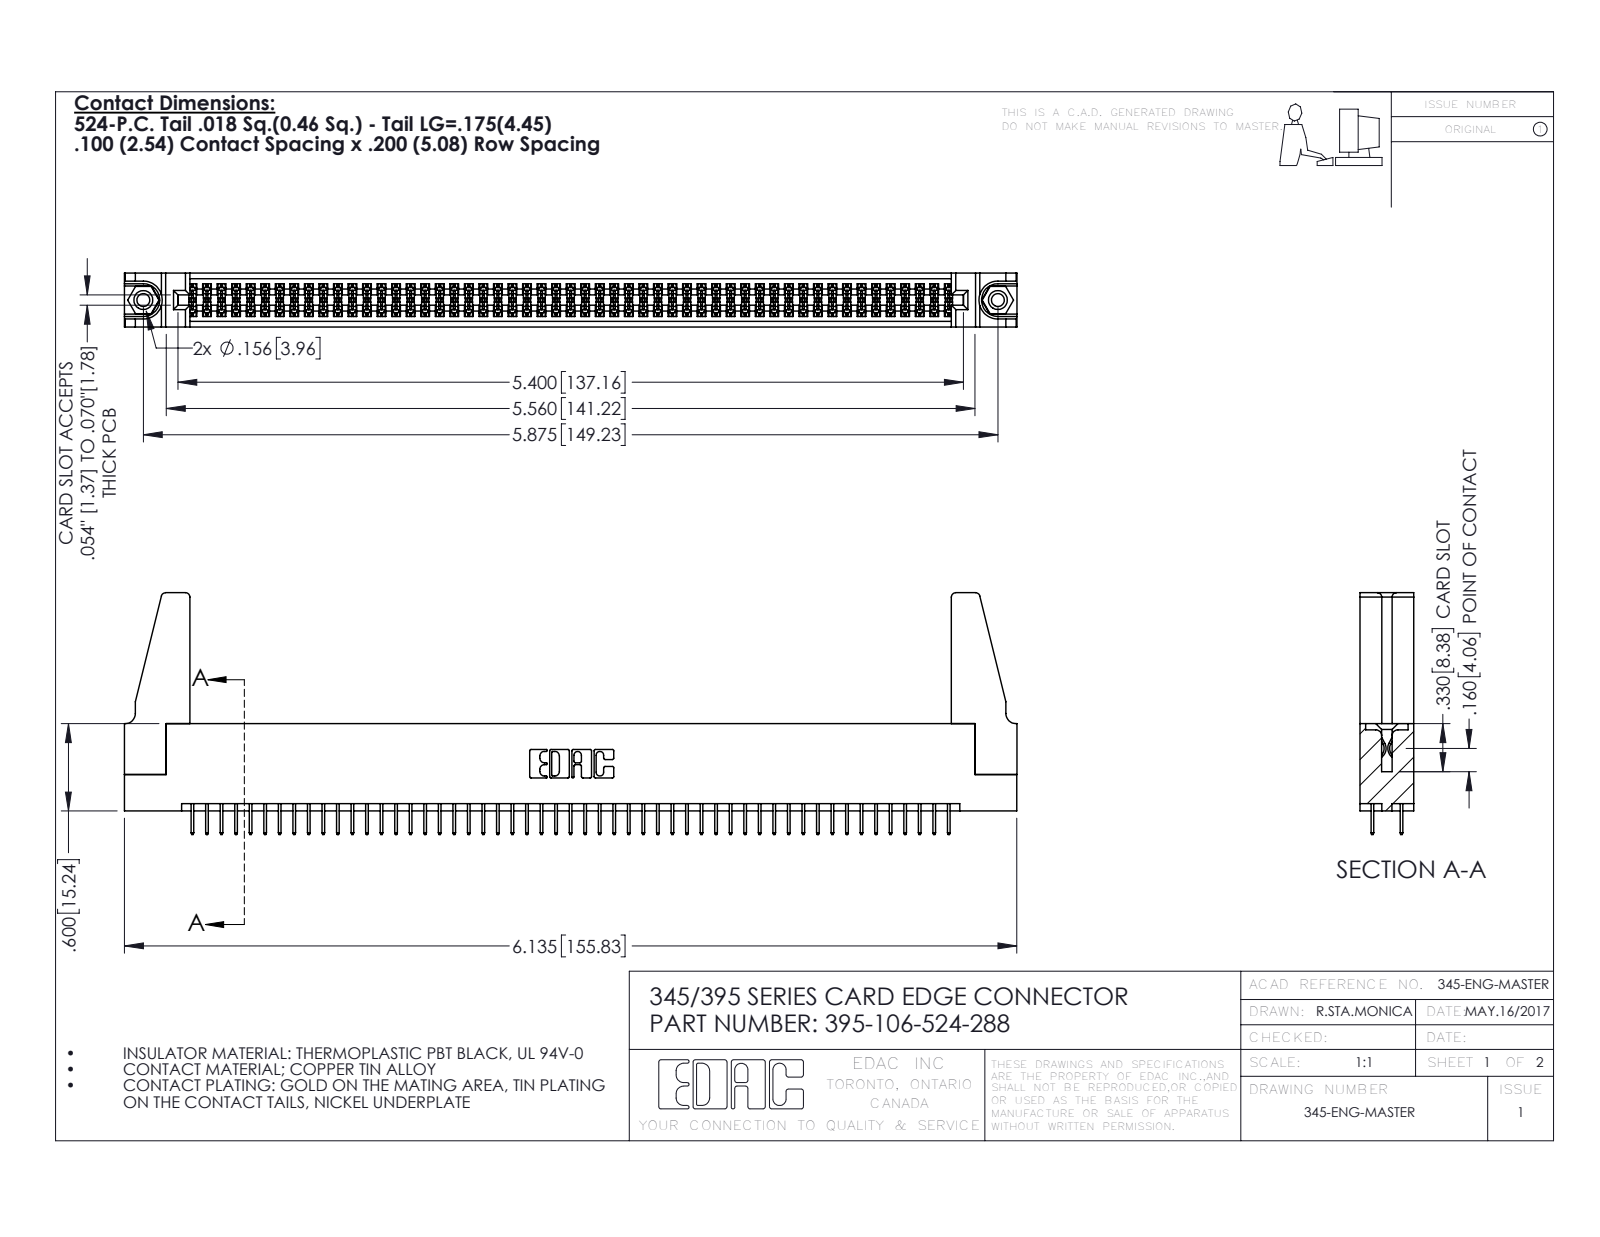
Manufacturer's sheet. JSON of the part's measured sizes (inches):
{"part_name": "395-106-524-288; 345 Part_Flush Mounting Lugs - 0.156 Dia-TH; 345-220-078_345-220-088; 345-292-001_345-293-124 (+1 more)", "step_written_by": "SolidWorks 2016 (CONFIG_CONTROL_DESIGN)", "units": "inches", "bodies": {"solids": 111, "faces": 5974, "planar": 4286, "cylindrical": 1672, "other": 16}, "overall_size": [6.136, 1.662, 0.37], "volume_in3": 1.119, "surface_area_in2": 39.07, "round_holes": [[0.089, 2], [0.125, 2], [0.156, 2], [0.064, 1]], "round_bosses_or_shafts": [[0.155, 2]], "partial_cylinders_radius": [[0.006, 159], [0.01, 22], [0.03, 8], [0.007, 6], [0.031, 6], [0.026, 3], [0.014, 2], [0.019, 2]], "face_to_face_distances": [0.072, 0.298, 0.37, 0.2, 0.098, 0.272, 0.025, 0.225, 0.072, 0.175], "hole_center_spacings": [0.27, 5.639, 5.875]}
